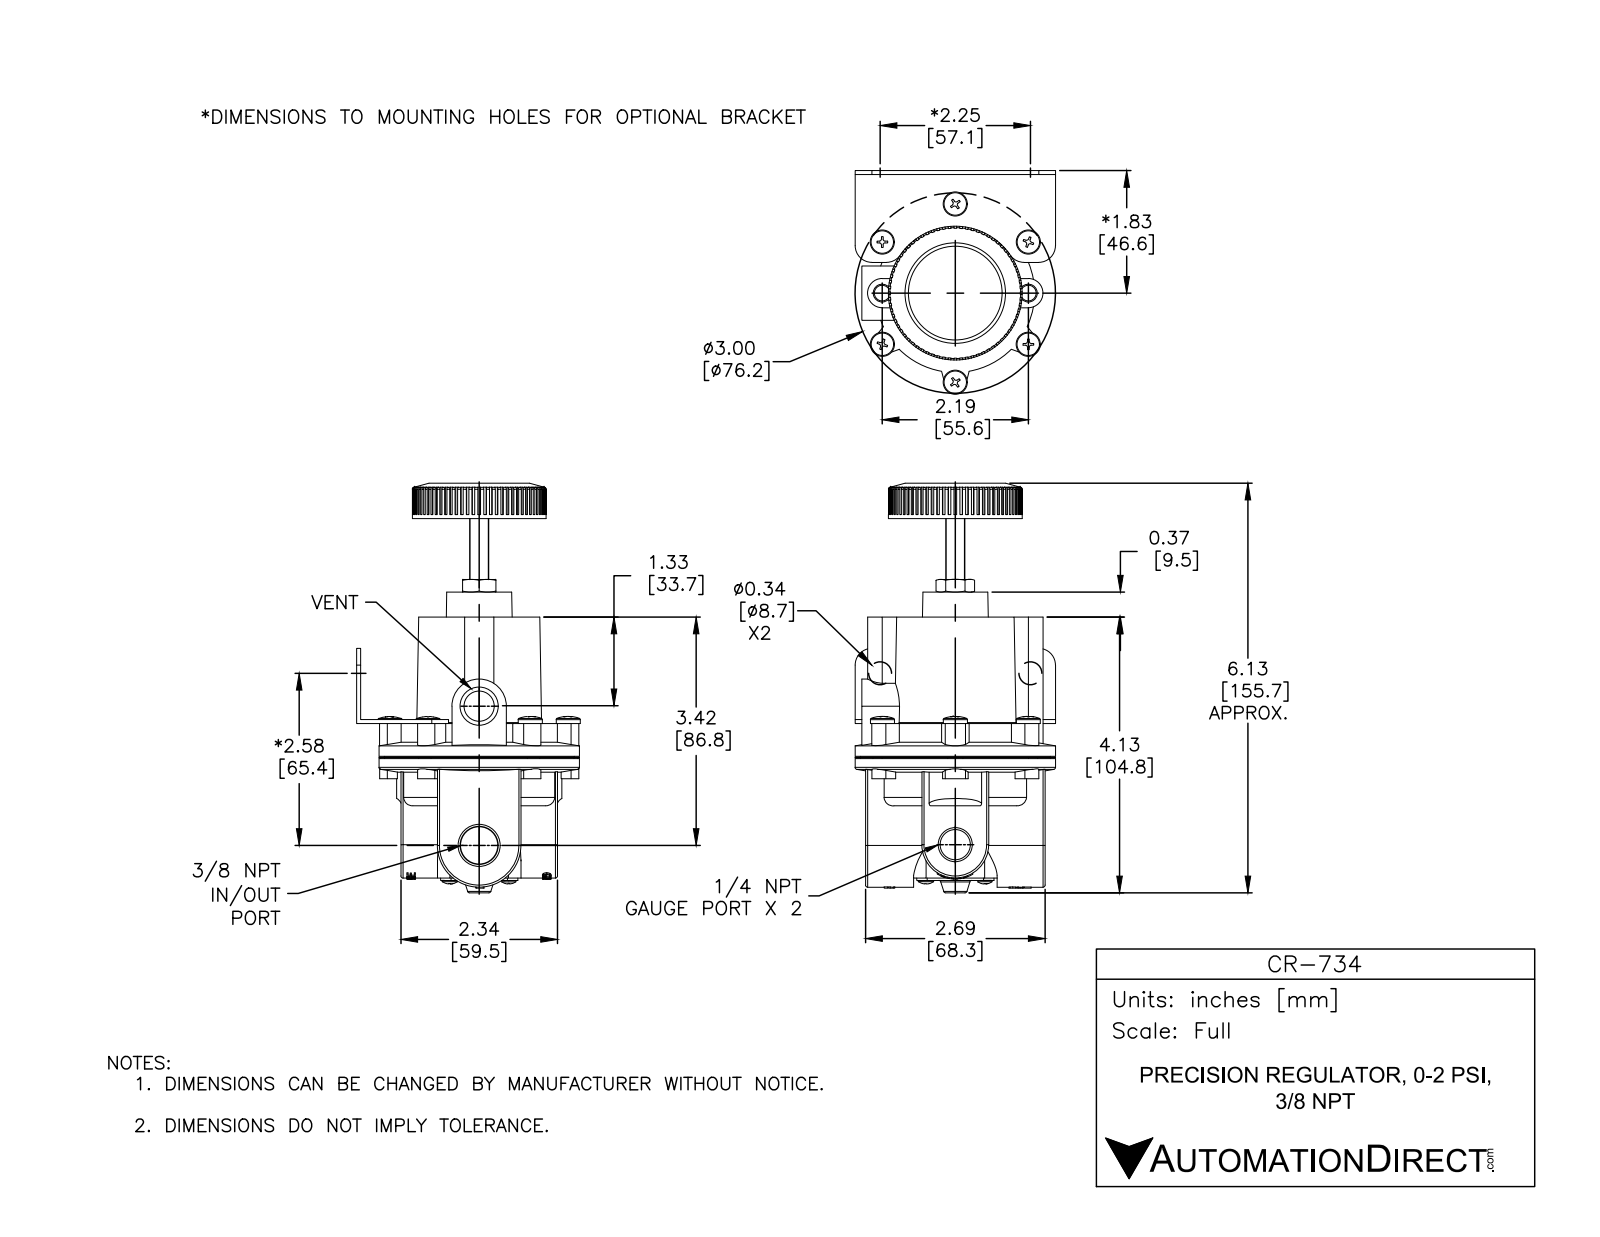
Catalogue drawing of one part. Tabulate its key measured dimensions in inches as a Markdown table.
| quantity | value |
| --- | --- |
| part name | CR-734 |
| STEP written by | SolidWorks 2015 (CONFIG_CONTROL_DESIGN) |
| units | inches |
| bodies | 10 solids, 1525 faces (521 planar, 817 cylindrical, 187 other) |
| overall size | 6.123 × 3.041 × 3 |
| volume | 17.33 in³ |
| surface area | 88.44 in² |
| round holes (diameter × count) | 0.201 × 8, 0.159 × 6, 0.438 × 2, 0.562 × 1, 1.403 × 1, 1.683 × 1 |
| round bosses / shafts (diameter × count) | 0.373 × 6, 0.19 × 6, 0.149 × 6, 3 × 1, 2 × 1, 0.628 × 1, 0.281 × 1 |
| partial cylindrical surfaces (radius × count) | 0.004 × 72, 0.02 × 18, 0.032 × 6, 0.156 × 6, 0.157 × 6, 0.141 × 4, 0.187 × 3, 0.033 × 2 |
| main face-to-face distances | 0.034, 2.114, 2.08, 0.524, 0.49, 1.59, 3.879, 3.845, 3.355, 1.765 |
| hole center spacings | 1.334, 1.725, 2.317, 0.765, 0.765, 1.094, 1.232, 1.232 |
